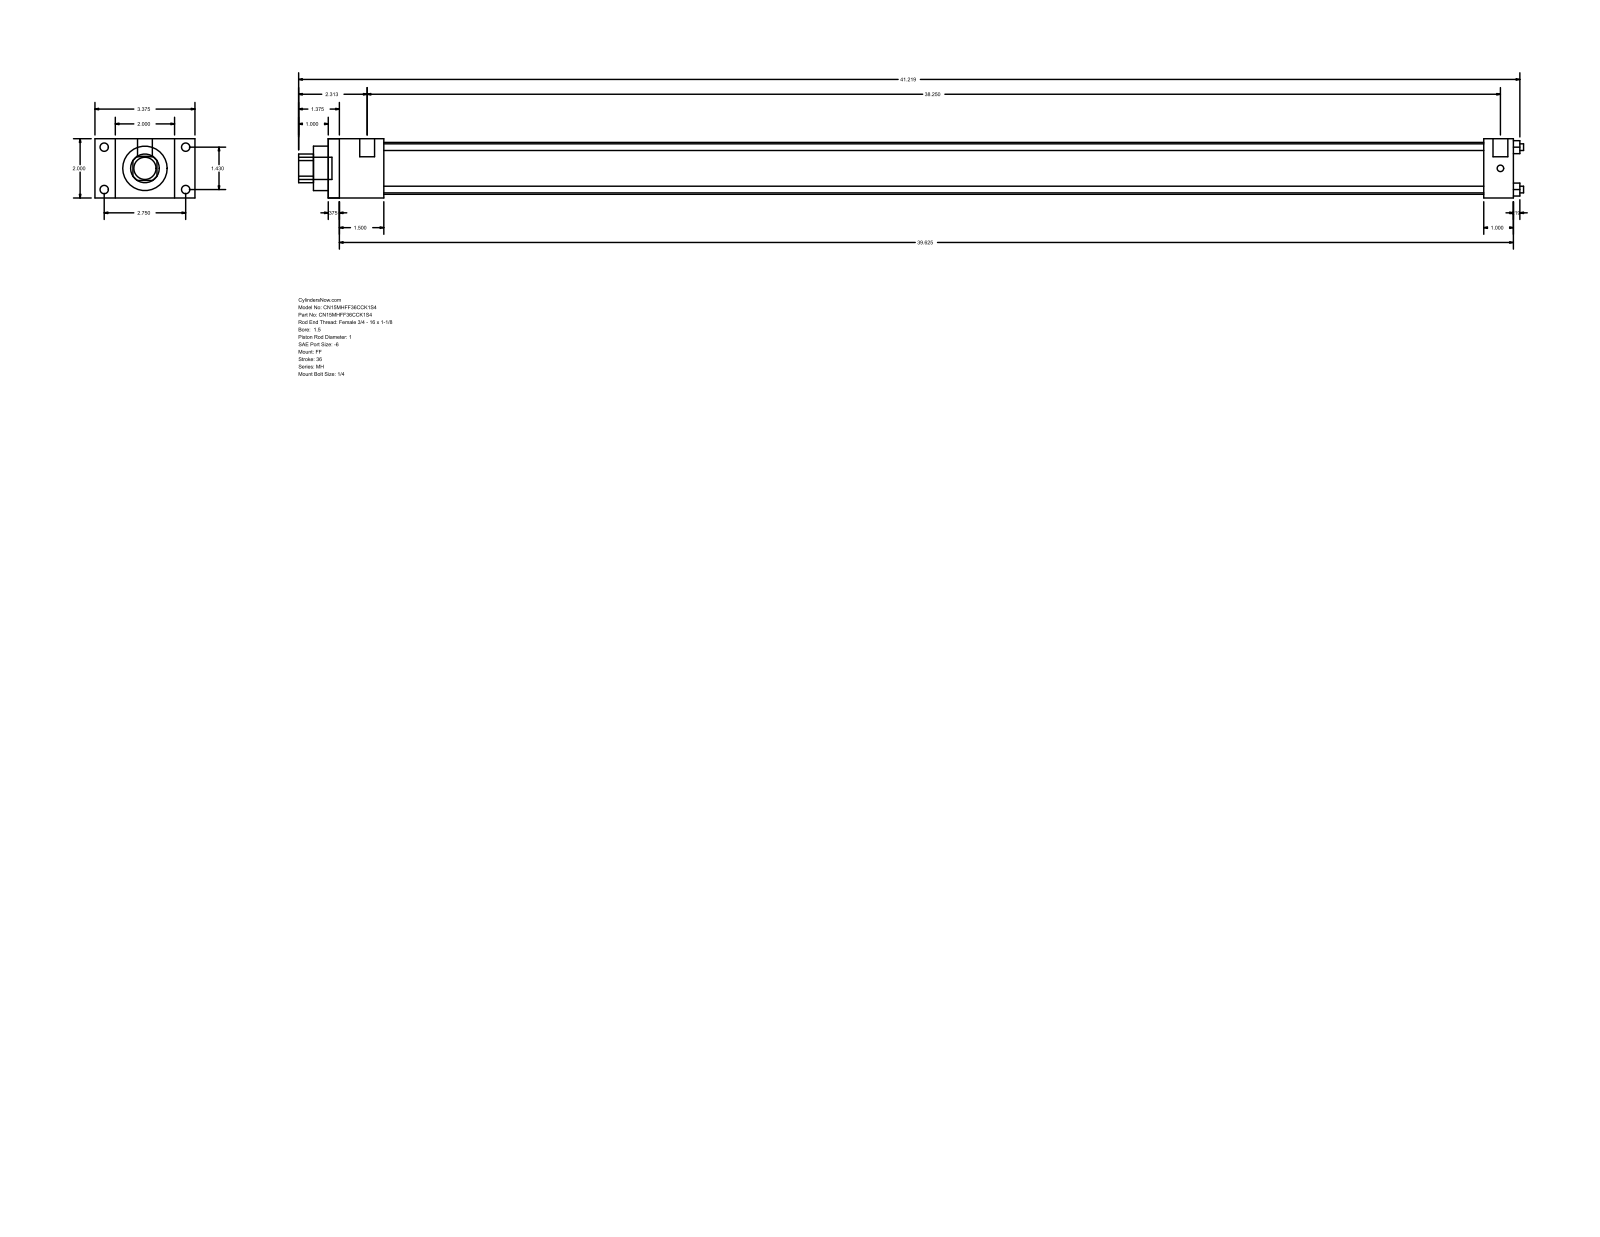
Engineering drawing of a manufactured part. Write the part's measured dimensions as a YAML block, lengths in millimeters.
part_name: "MH_FF__0150_1"
step_written_by: "GSSL Pune (CONFIG_CONTROL_DESIGN)"
units: millimeters
bodies: {solids: 0, faces: 92, planar: 64, cylindrical: 28, other: 0}
overall_size: [1050.13, 85.72, 50.8]
round_holes:
  - {diameter: 5.71, count: 4}
  - {diameter: 25.4, count: 1}
  - {diameter: 38.1, count: 1}
  - {diameter: 44.45, count: 1}
round_bosses_or_shafts:
  - {diameter: 7.14, count: 4}
  - {diameter: 5.56, count: 4}
  - {diameter: 12.7, count: 2}
  - {diameter: 19.05, count: 1}
partial_cylinders:
  - {radius: 12.29, count: 1}
face_to_face_distances: [50.8, 1016, 9.52, 1006.48, 25.4, 17.46, 68.26, 47.63, 38.11, 968.37]
hole_center_spacings: [25.68, 36.32, 51.36]
